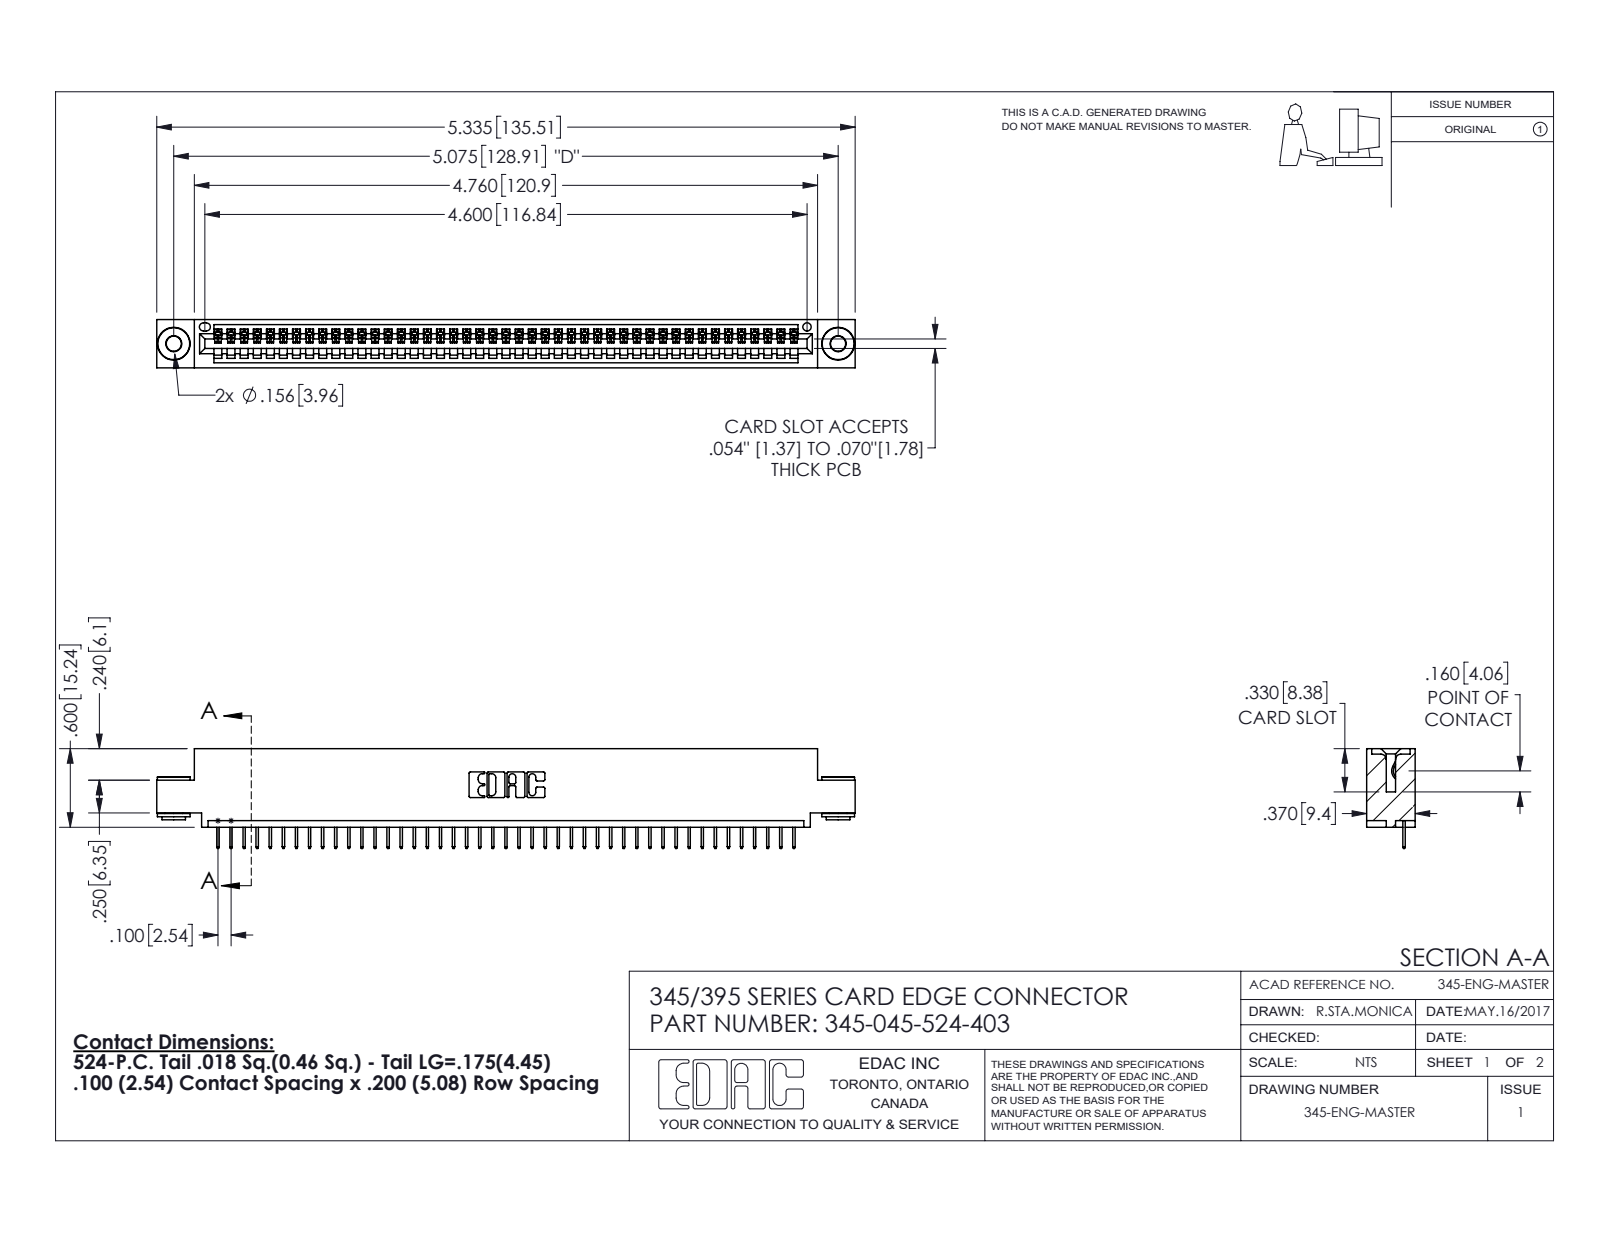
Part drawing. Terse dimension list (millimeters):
name: 345-292-001_345-293-124; 345-045-524-403; 345 Part_0.110 Offset - 0.156 Dia-TH; 345-250-002_345-250-002-102
written by: SolidWorks 2016 (CONFIG_CONTROL_DESIGN)
unit: mm
bodies: 48 solids, 2958 faces (2164 planar, 786 cylindrical, 8 other)
size: 135.5 × 19.4 × 9.4
volume: 12 700 mm³; area: 16 600 mm²
holes: 2× ⌀2.9, 2× ⌀4, 1× ⌀1.6
bosses: 2× ⌀6.4, 2× ⌀4.6, 2× ⌀3.5
rounds: 90× R0.2, 22× R0.3, 6× R0.2, 6× R0.8, 3× R0.7, 2× R0.8, 2× R1, 1× R0.4
face distances: 1.8, 7.6, 9.4, 5.1, 0.6, 2.5, 6.9, 5.7, 1.8, 3.8
hole spacings: 6.9, 122.9, 128.9
